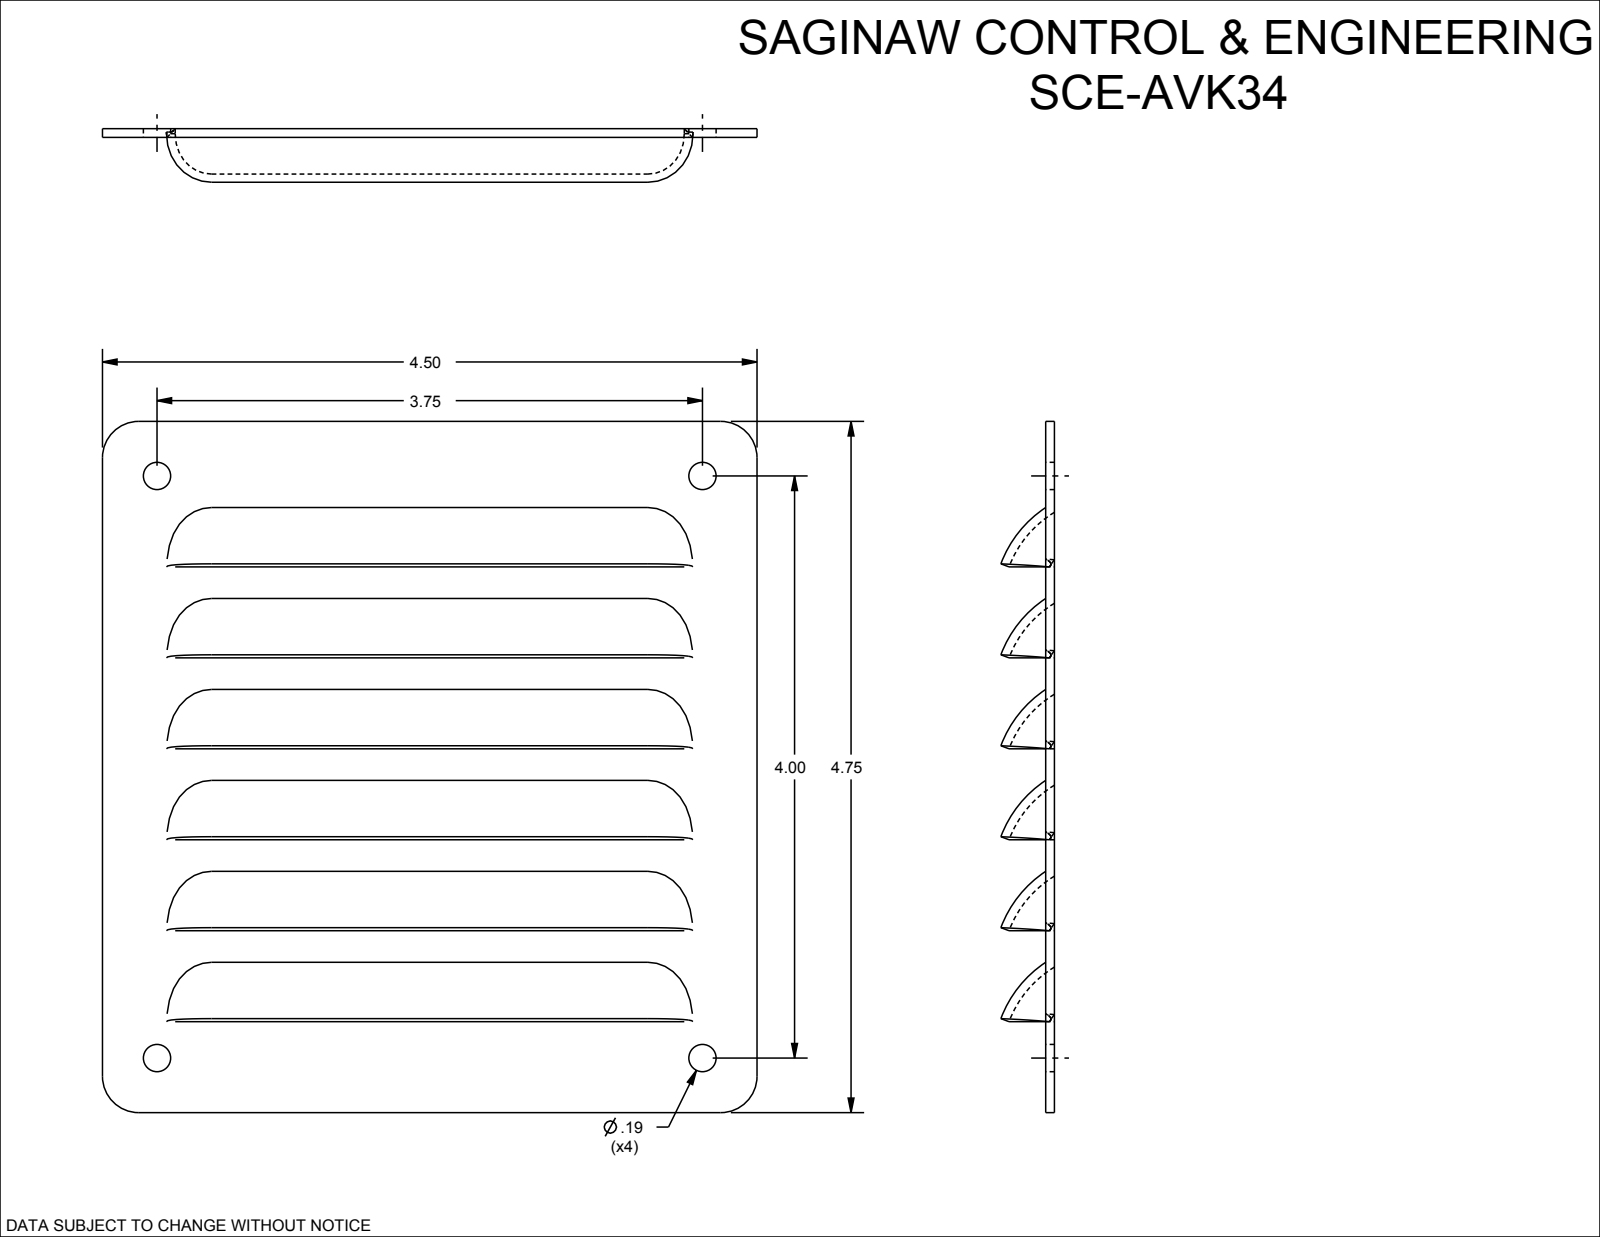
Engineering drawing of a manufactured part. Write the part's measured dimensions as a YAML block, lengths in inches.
part_name: "SCE-AVK34"
step_written_by: "SolidWorks 2021 (AUTOMOTIVE_DESIGN)"
units: inches
bodies: {solids: 1, faces: 108, planar: 24, cylindrical: 36, other: 48}
overall_size: [4.75, 4.5, 0.467]
volume: 1.458
surface_area: 52.12
round_holes:
  - {diameter: 0.187, count: 4}
partial_cylinders:
  - {radius: 0.74, count: 6}
  - {radius: 0.8, count: 6}
  - {radius: 0.25, count: 4}
face_to_face_distances: [0.06, 1.25, 0.625, 0.625, 0.29, 0.96, 2.5, 1.171, 1.875, 1.875]
hole_center_spacings: [3.75, 4, 5.483]
